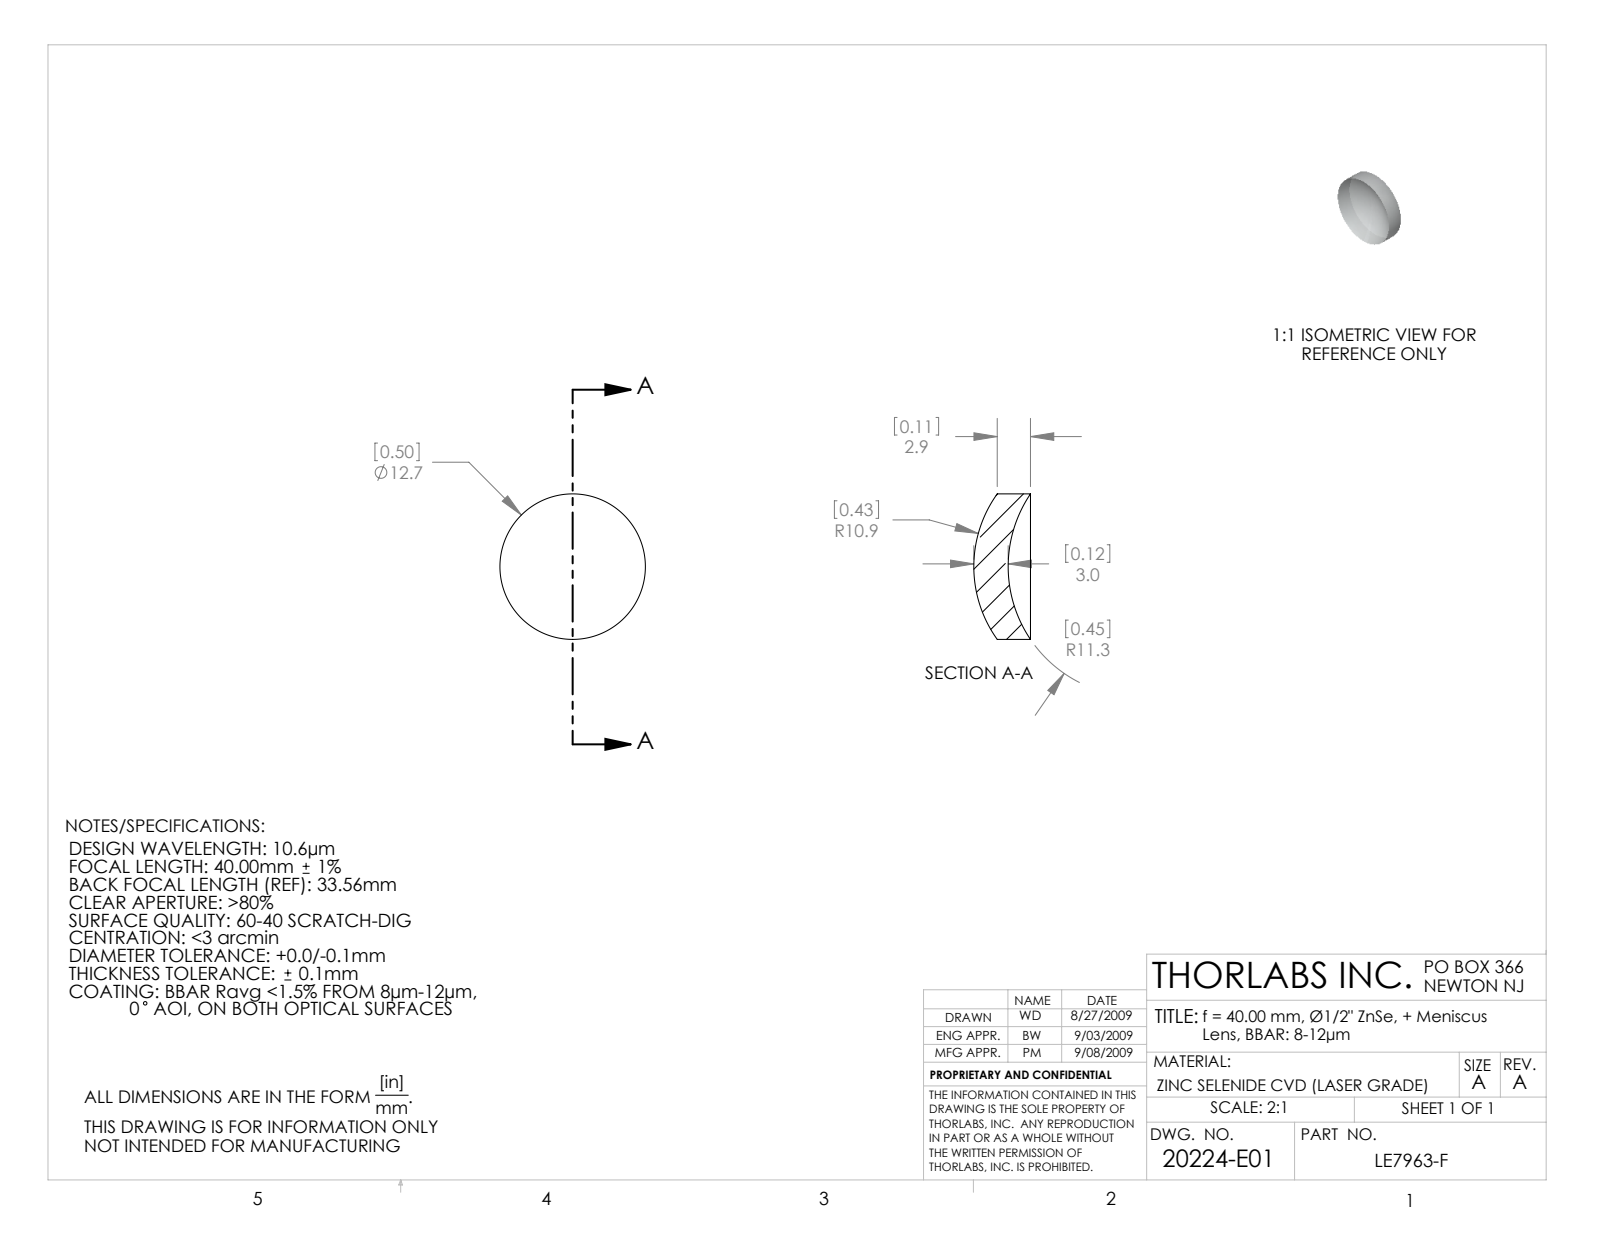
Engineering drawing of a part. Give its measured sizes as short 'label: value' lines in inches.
name: 20224-E0W
written by: SolidWorks 2007 (CONFIG_CONTROL_DESIGN)
unit: in
bodies: 1 solid, 6 faces (0 planar, 2 cylindrical, 4 other)
size: 0.5 × 0.5 × 0.195
volume: 0.023 in³; area: 0.611 in²
bosses: 1× ⌀0.5
